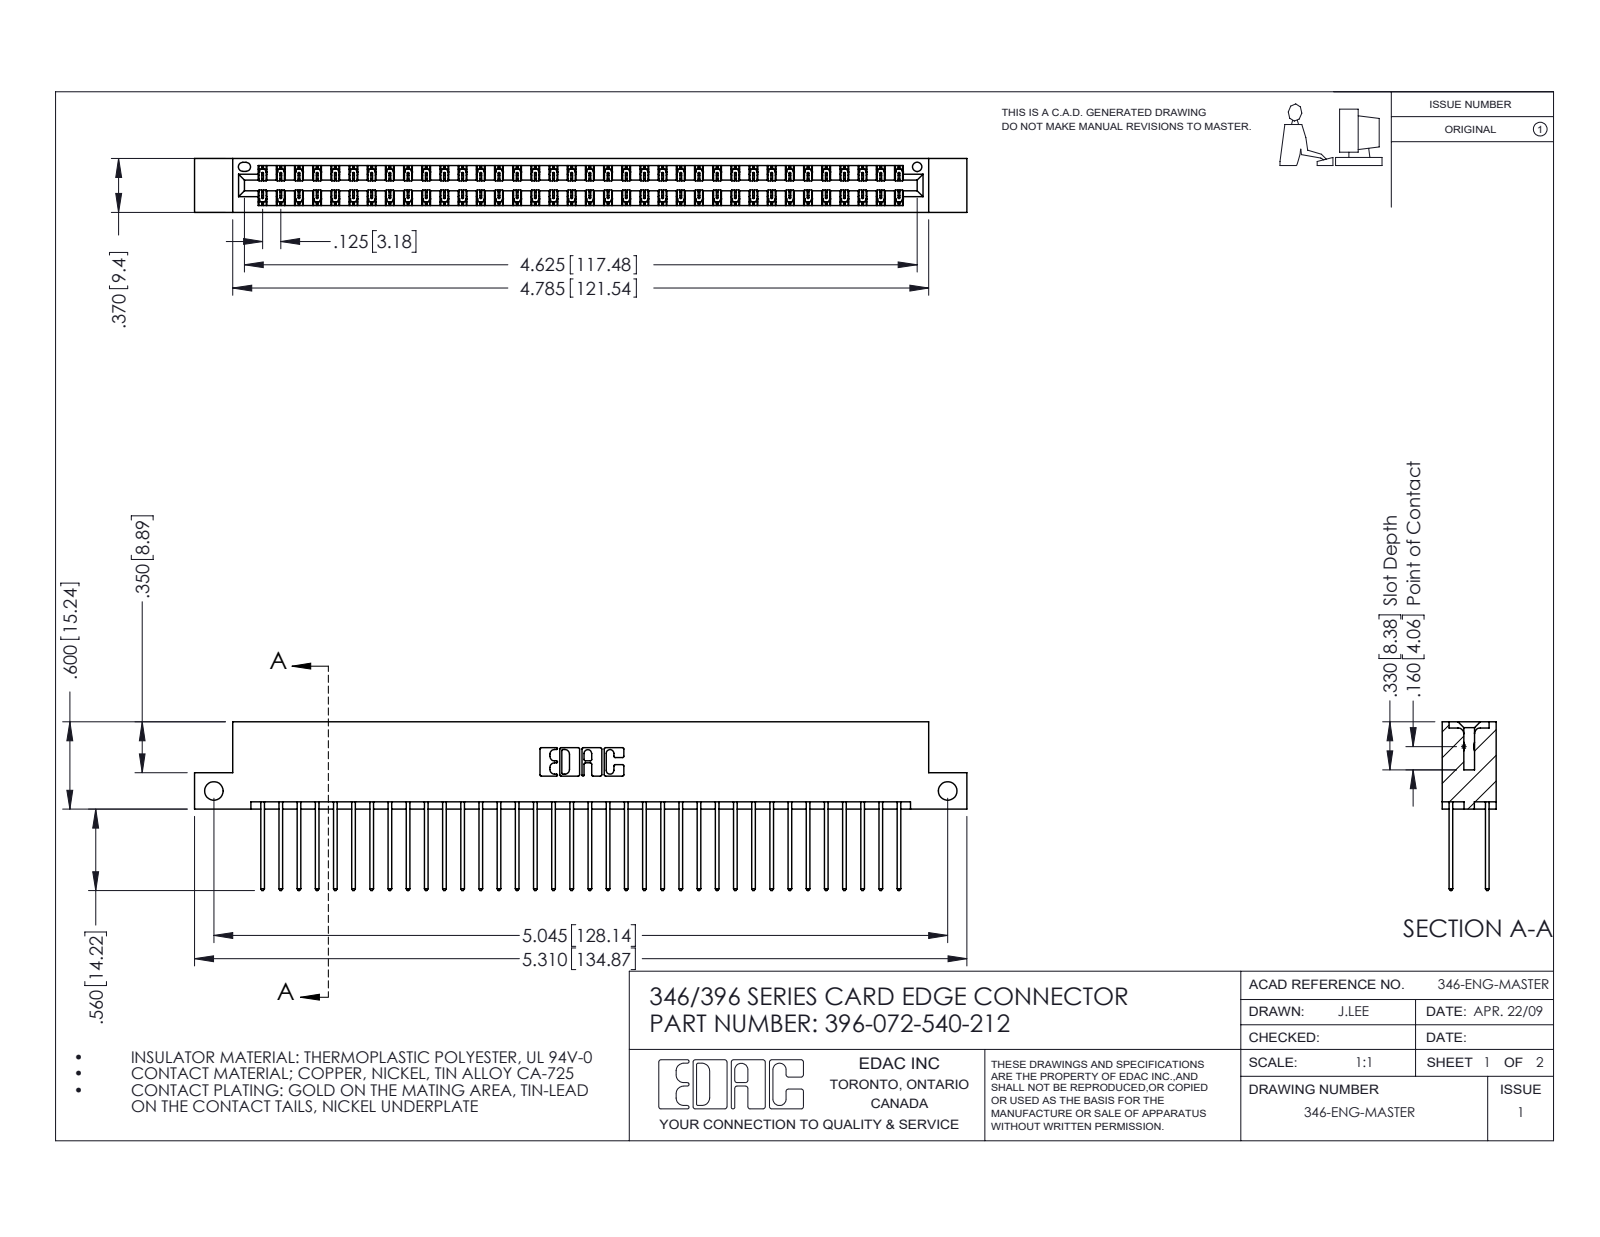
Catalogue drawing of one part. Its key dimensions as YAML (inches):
part_name: "345-292-001_345-293-140; 396-072-540-212; 346 Part_Flush Mounting Lugs - Side Mount"
step_written_by: "SolidWorks 2016 (CONFIG_CONTROL_DESIGN)"
units: inches
bodies: {solids: 73, faces: 3866, planar: 2596, cylindrical: 1270, other: 0}
overall_size: [5.31, 1.16, 0.37]
volume: 0.811
surface_area: 29.96
round_holes:
  - {diameter: 0.128, count: 2}
  - {diameter: 0.064, count: 1}
partial_cylinders:
  - {radius: 0.006, count: 108}
  - {radius: 0.01, count: 72}
  - {radius: 0.01, count: 22}
  - {radius: 0.007, count: 6}
  - {radius: 0.031, count: 6}
  - {radius: 0.026, count: 3}
  - {radius: 0.014, count: 2}
  - {radius: 0.022, count: 2}
face_to_face_distances: [0.048, 0.322, 0.25, 0.072, 0.298, 0.025, 0.37, 0.275, 0.148, 0.222]
hole_center_spacings: [5.045]
